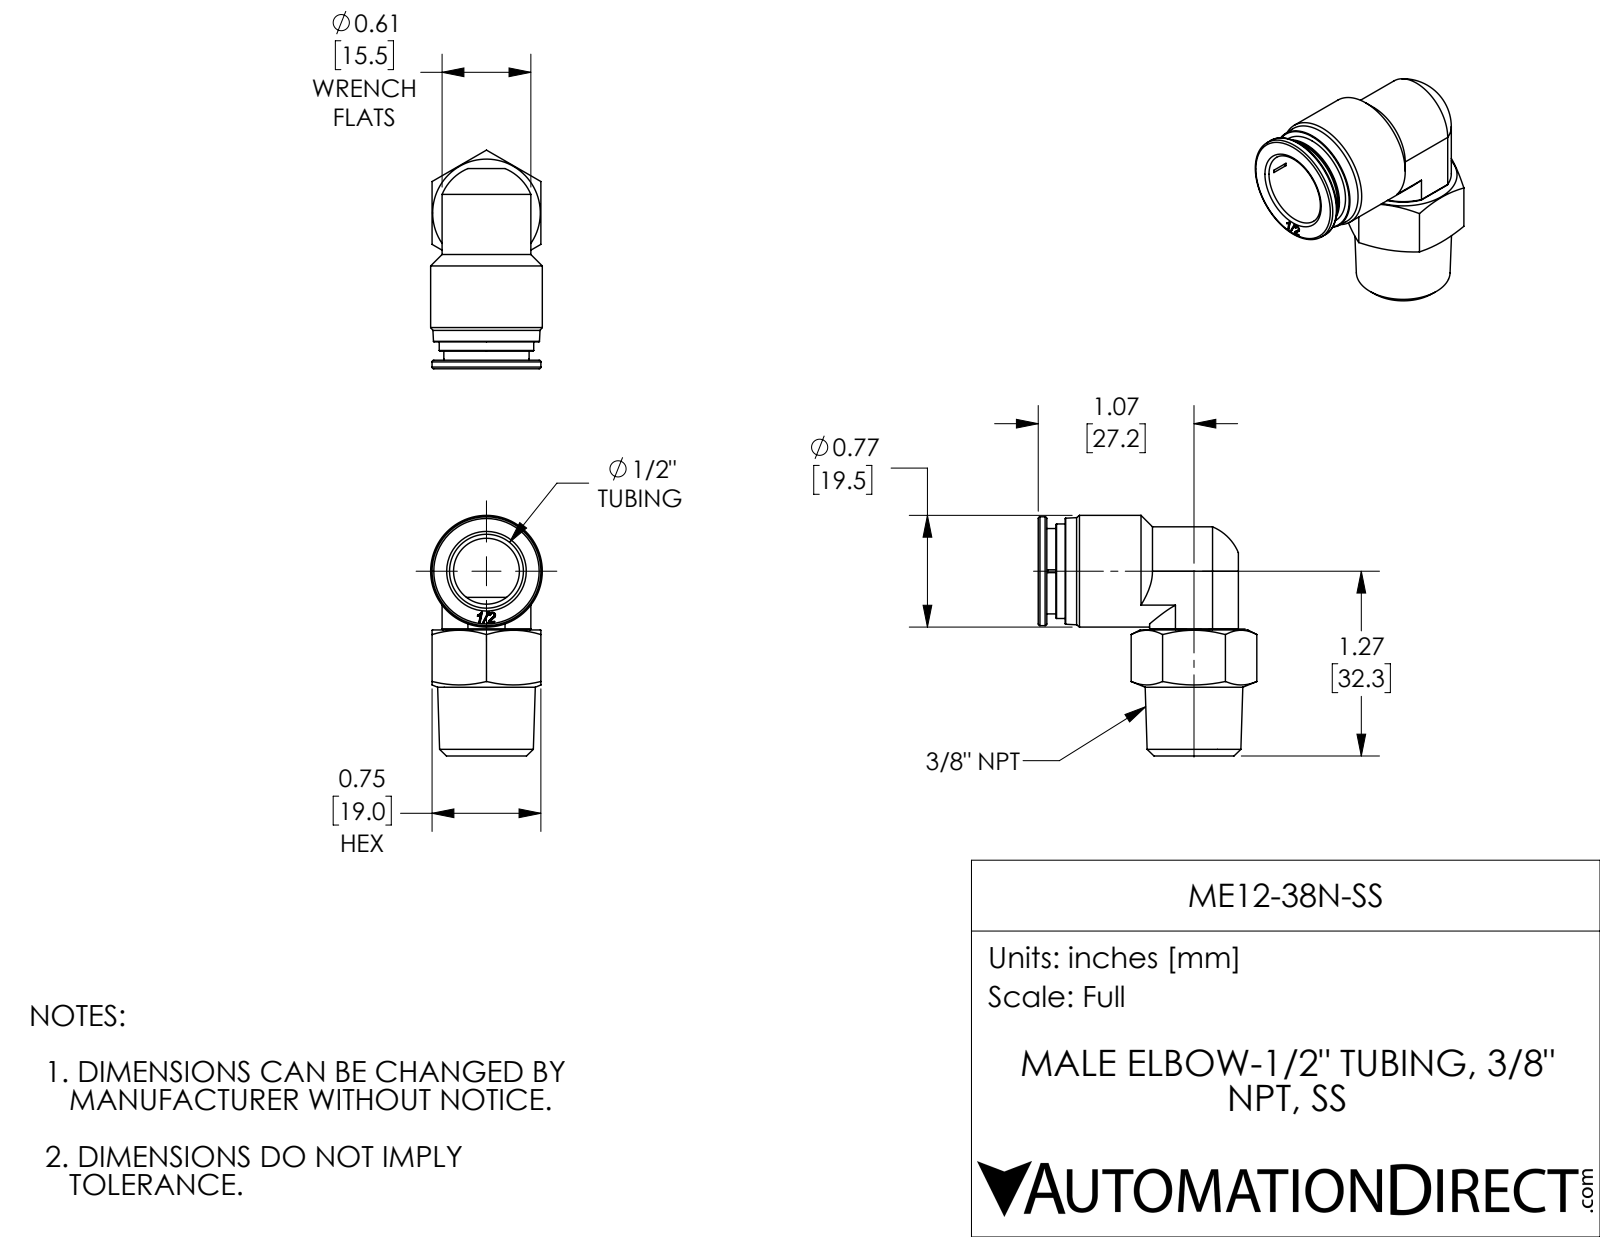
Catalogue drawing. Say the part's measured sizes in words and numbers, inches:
The part is named "ME12-38N-SS". Its 3-D file was written by "SolidWorks 2017 (AUTOMOTIVE_DESIGN)". It is 2 solids with 128 faces: 43 planar, 31 cylindrical and 54 other. Overall it measures 1.654 by 1.503 by 0.768 inches. Its volume is 0.594 cubic inches and its surface area 10.5 square inches. Round holes: 1 of diameter 0.276, 1 of diameter 0.356, 1 of diameter 0.453, 1 of diameter 0.508, 1 of diameter 0.594. Round bosses or shafts: 1 of diameter 0.768, 1 of diameter 0.748, 1 of diameter 0.65, 1 of diameter 0.587, 1 of diameter 0.354. Partial cylindrical surfaces (rounded edges, fillets, slot ends): 4 of radius 0.008, 1 of radius 0.305, 1 of radius 0.331. The main face-to-face distances are 0.748, 0.069, 0.679, 0.866, 0.61, 0.059, 1.376, 1.317, 0.185, 0.126.
